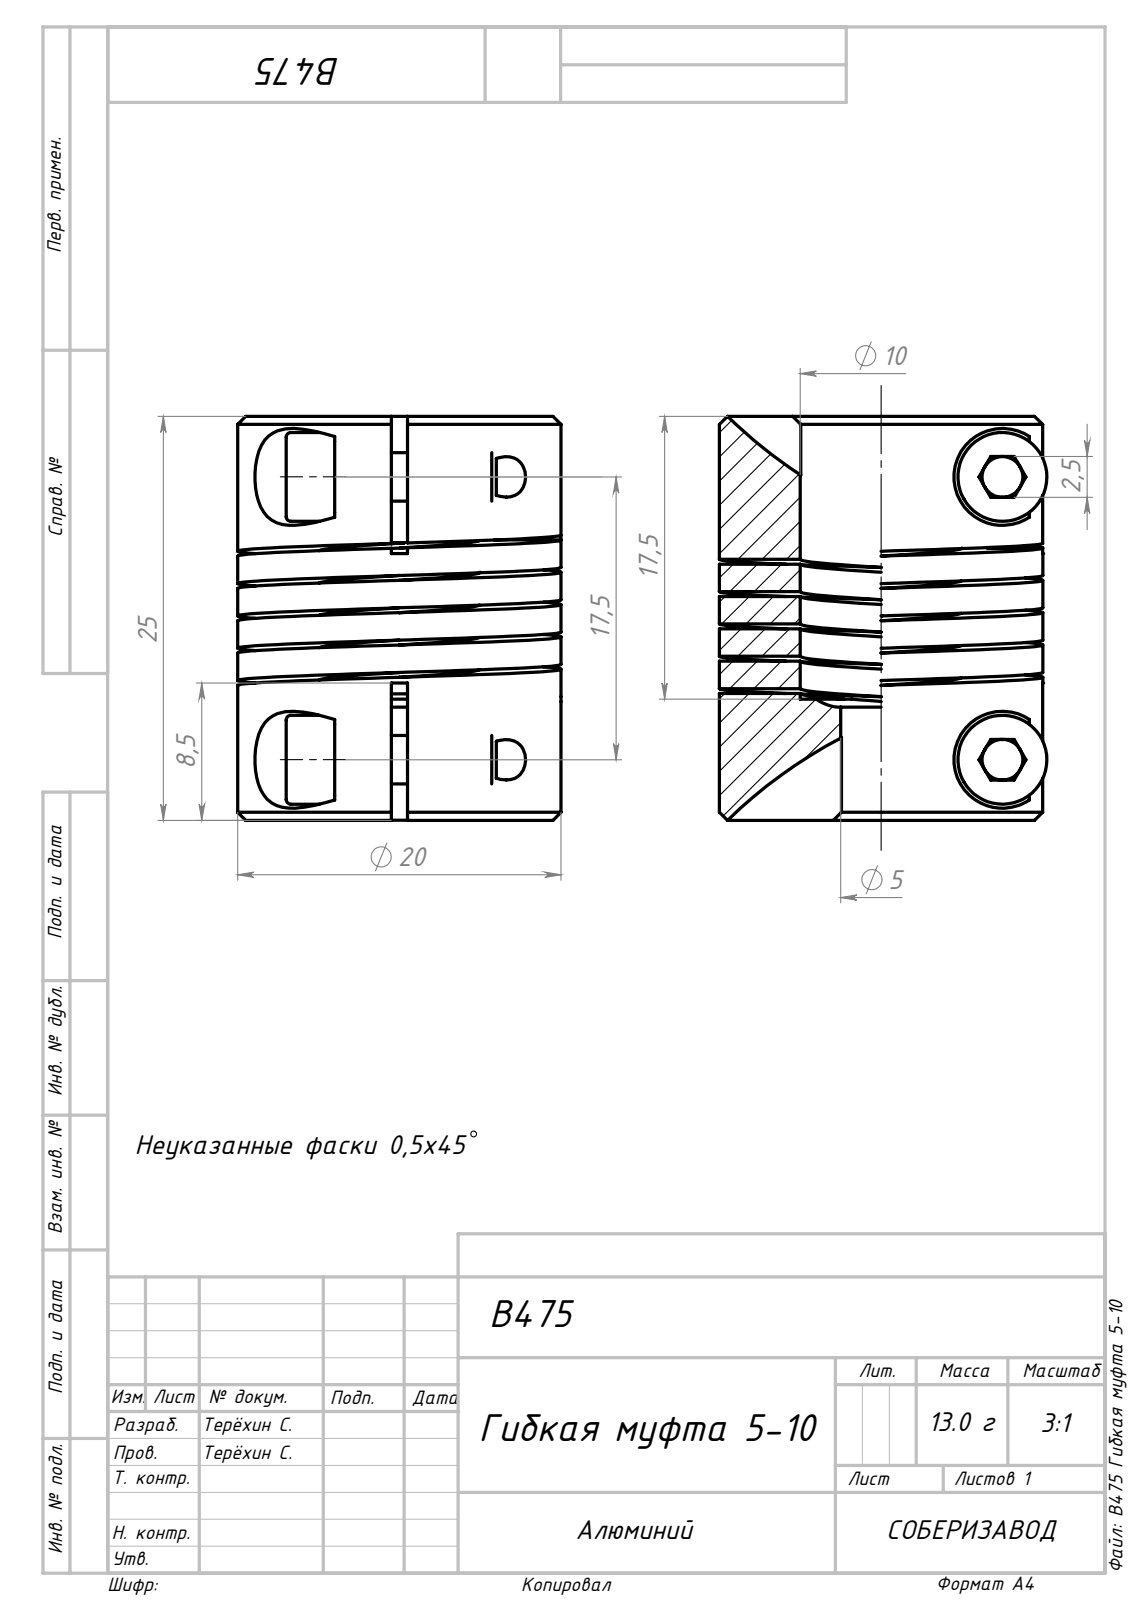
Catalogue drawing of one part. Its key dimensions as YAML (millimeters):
part_name: "socket head cap screw_din_DIN 912 M3 x 10 --- 10N; B475 Гибкая муфта 5-10; B475 Гибкая муфта 5-10_00"
step_written_by: "SolidWorks 2022 (AUTOMOTIVE_DESIGN)"
units: millimeters
bodies: {solids: 3, faces: 140, planar: 50, cylindrical: 56, other: 34}
overall_size: [25, 20.25, 20]
volume: 5858
surface_area: 5768
round_holes:
  - {diameter: 2.5, count: 2}
  - {diameter: 5, count: 1}
  - {diameter: 10, count: 1}
round_bosses_or_shafts:
  - {diameter: 5.5, count: 2}
  - {diameter: 3, count: 2}
  - {diameter: 20, count: 1}
partial_cylinders:
  - {radius: 3, count: 2}
  - {radius: 30, count: 2}
face_to_face_distances: [25, 1, 4.5, 3.5, 7.5, 6.5, 17.5, 3, 2.52, 5.5]
hole_center_spacings: [17.5]
